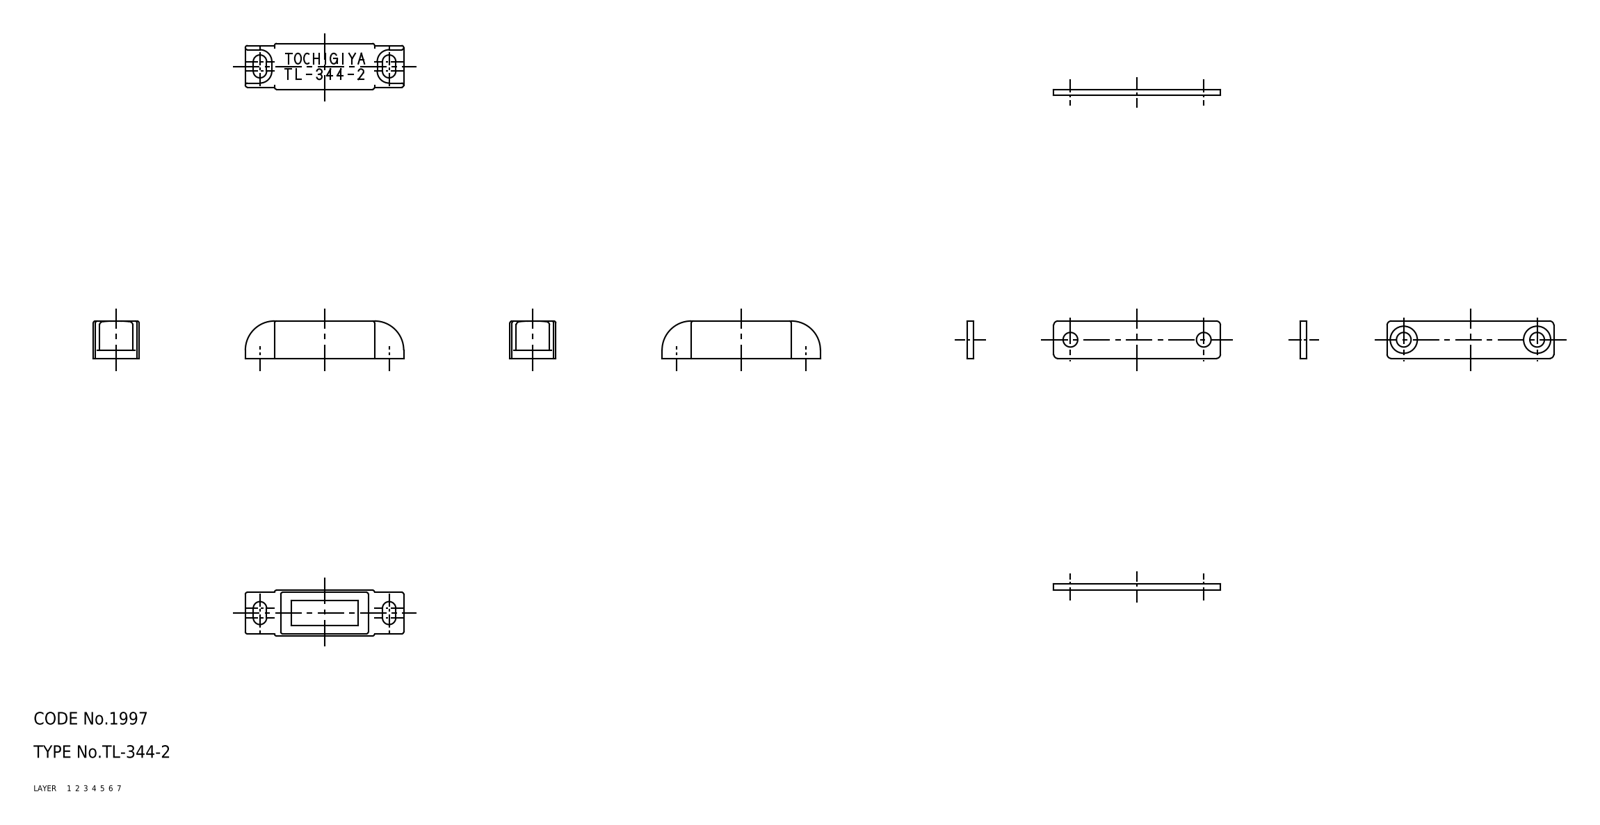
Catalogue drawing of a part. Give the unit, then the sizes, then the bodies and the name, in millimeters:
Units: millimetres
Overall size (bounding box): 40 × 24.5 × 9
Volume: 3 337 mm³ · Surface area: 3 238 mm²
Bodies: 3 solids, 97 faces (0 planar, 0 cylindrical, 97 other)
Part name (STEP PRODUCT): keeper; housing; cover; TL_344_2_12318_36
STEP written by: CADfix (AUTOMOTIVE_DESIGN)
